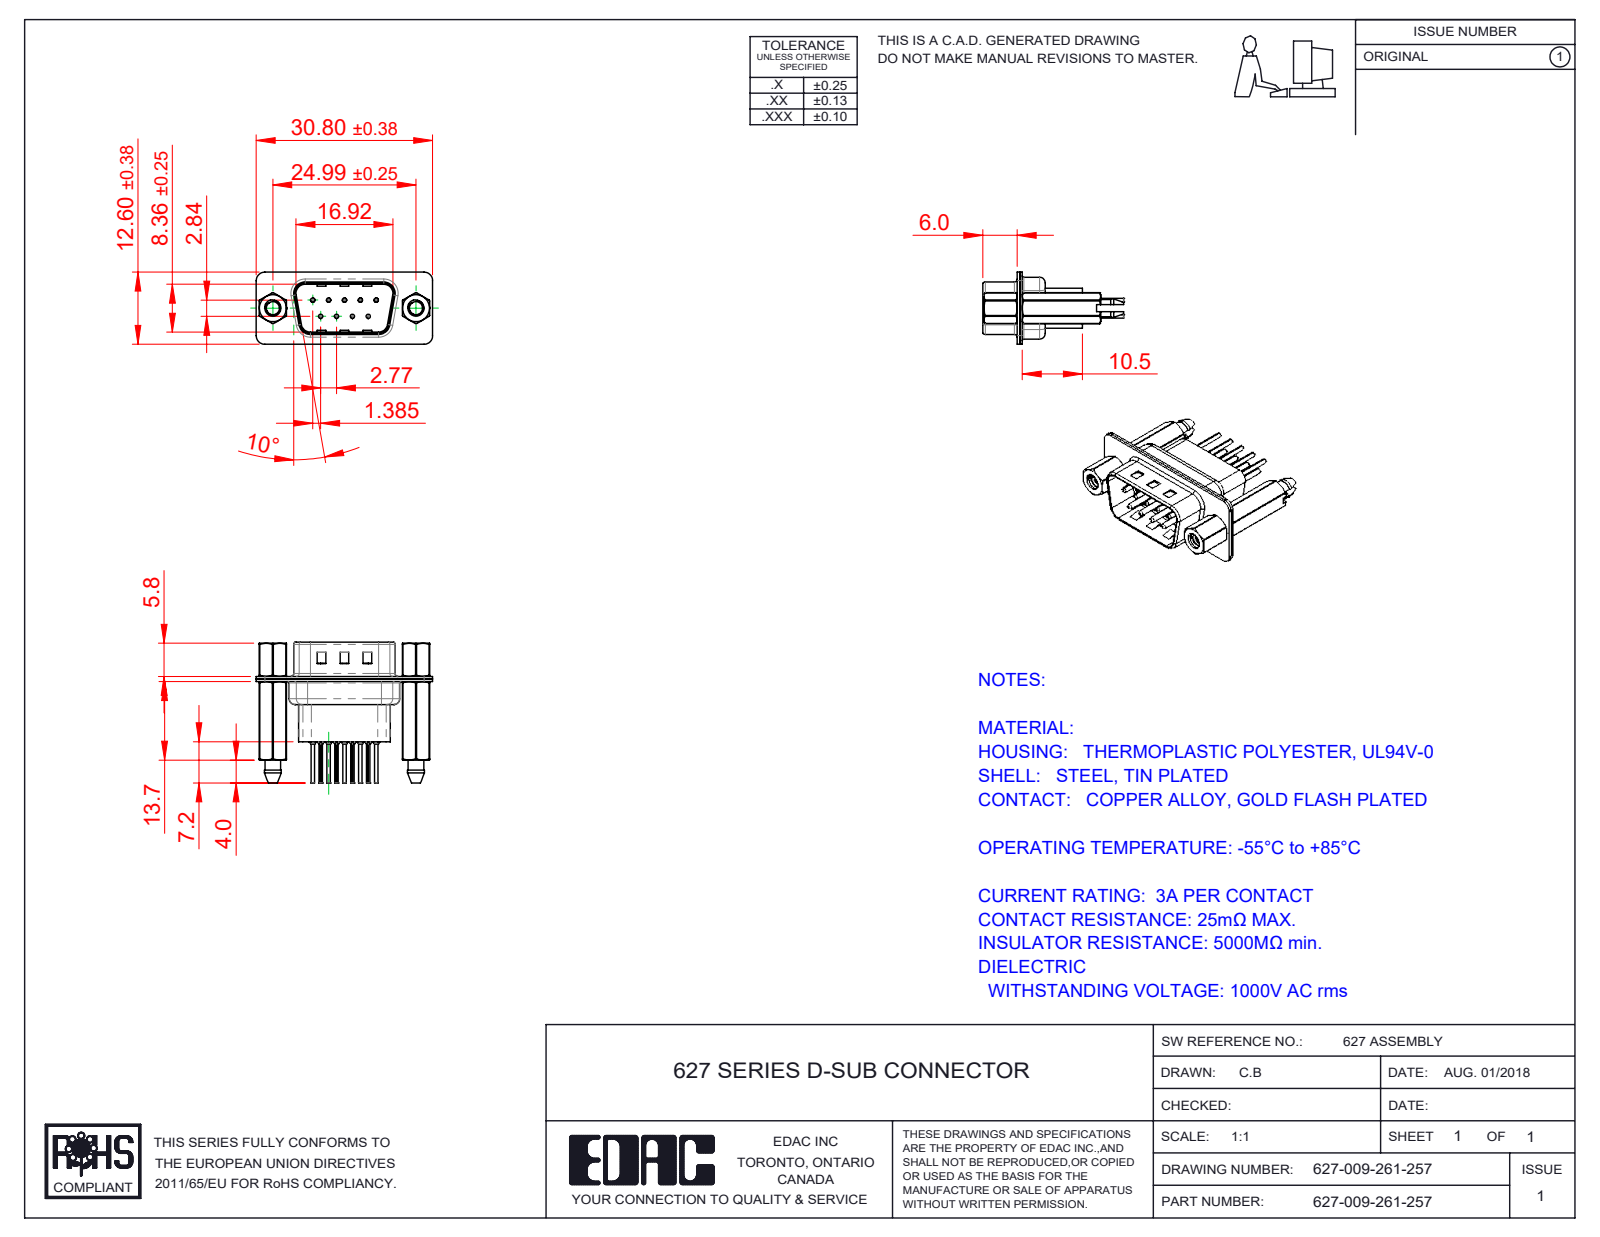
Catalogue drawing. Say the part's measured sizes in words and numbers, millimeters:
The part is named "627 Contact Row 1_61; 627-009-261-057; 627 Contact Row 2_61; 627 Housing_09 HP (+4 more)". Its 3-D file was written by "SolidWorks 2020 (CONFIG_CONTROL_DESIGN)". It is 16 solids with 1420 faces: 377 planar, 600 cylindrical and 443 other. Overall it measures 30.8 by 24.6 by 12.6 millimeters. Its volume is 2 335 cubic millimeters and its surface area 5 999 square millimeters. Round holes: 9 of diameter 0.2, 9 of diameter 0.35, 9 of diameter 1.1, 9 of diameter 1.6, 2 of diameter 2.26, 2 of diameter 2.29, 2 of diameter 4, 2 of diameter 4.8. Round bosses or shafts: 9 of diameter 2, 9 of diameter 1.5, 9 of diameter 0.75, 9 of diameter 0.6, 2 of diameter 4.9, 2 of diameter 2.79. Partial cylindrical surfaces (rounded edges, fillets, slot ends): 20 of radius 1.5, 18 of radius 0.1, 12 of radius 2, 10 of radius 1.6, 8 of radius 0.5, 4 of radius 0.25, 4 of radius 0.6, 4 of radius 0.65. The main face-to-face distances are 0.45, 0.4, 0.9, 4.76, 0.82, 9.58, 1.4, 1.5, 0.68, 7.68. The hole center spacings are 3.16, 2.77, 5.54, 5.03, 5.04, 8.31, 7.48, 7.49.
